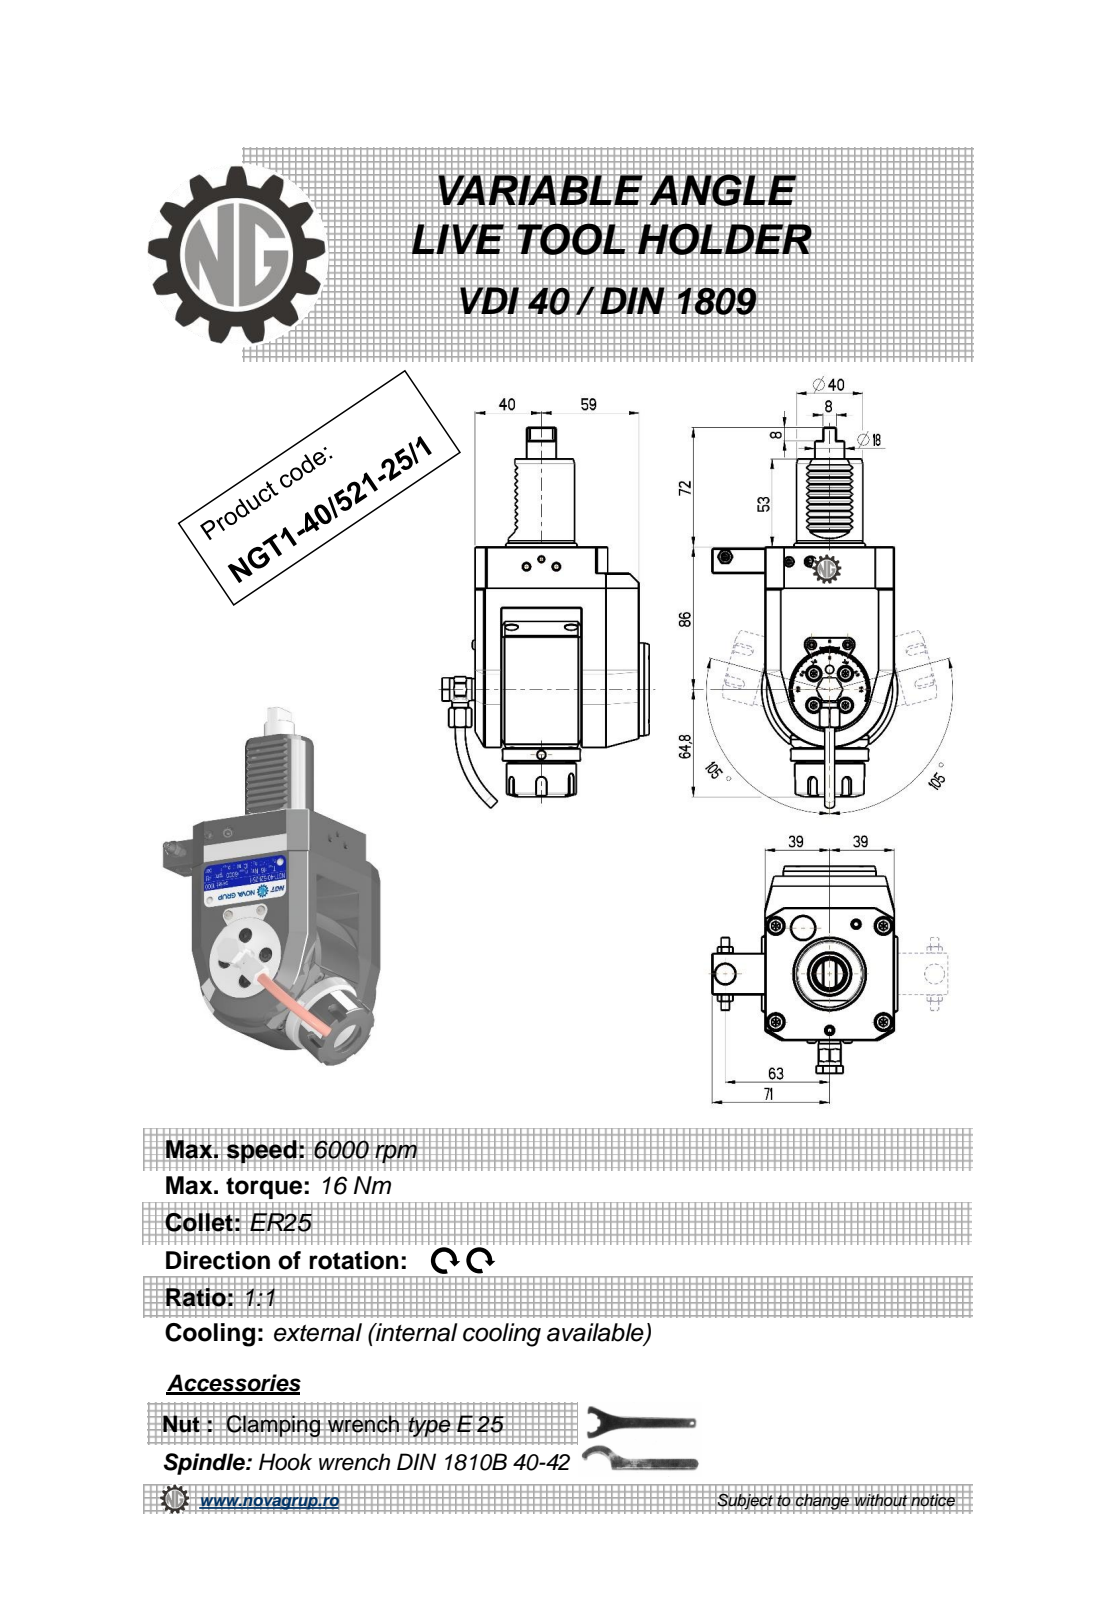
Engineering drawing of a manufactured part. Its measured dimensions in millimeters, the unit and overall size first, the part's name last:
Units: millimetres
Overall size (bounding box): 229.67 × 124.9 × 112
Round holes (diameter × count): ⌀4 ×3, ⌀5 ×2, ⌀3 ×1, ⌀4.2 ×1, ⌀6.2 ×1, ⌀9 ×1, ⌀9.5 ×1, ⌀11 ×1, ⌀12 ×1, ⌀20.3 ×1
Round bosses / shafts (diameter × count): ⌀10 ×2, ⌀6 ×2, ⌀5.7 ×2, ⌀82 ×1, ⌀56 ×1, ⌀47 ×1, ⌀42 ×1, ⌀40 ×1
Partial cylindrical surfaces — rounded edges, fillets, slot ends (radius × count): R0.26 ×12, R0.3 ×10, R0.16 ×6, R3 ×5, R0.5 ×4, R0.8 ×2, R1 ×2, R10 ×2
Main face-to-face distances: 16, 37, 99, 78, 64, 6, 105, 35, 21, 89
Hole centre spacings: 0.4, 39.45, 49, 49.4, 63, 79.81, 80.06, 101.83
Volume: 910 922 mm³ · Surface area: 83 610 mm²
Bodies: 1 solid, 575 faces (248 planar, 138 cylindrical, 189 other)
Part name (STEP PRODUCT): NGT1_40_521_25_1
STEP written by: PRO/ENGINEER BY PARAMETRIC TECHNOLOGY CORPORATION, 2010280 (CONFIG_CONTROL_DESIGN)
